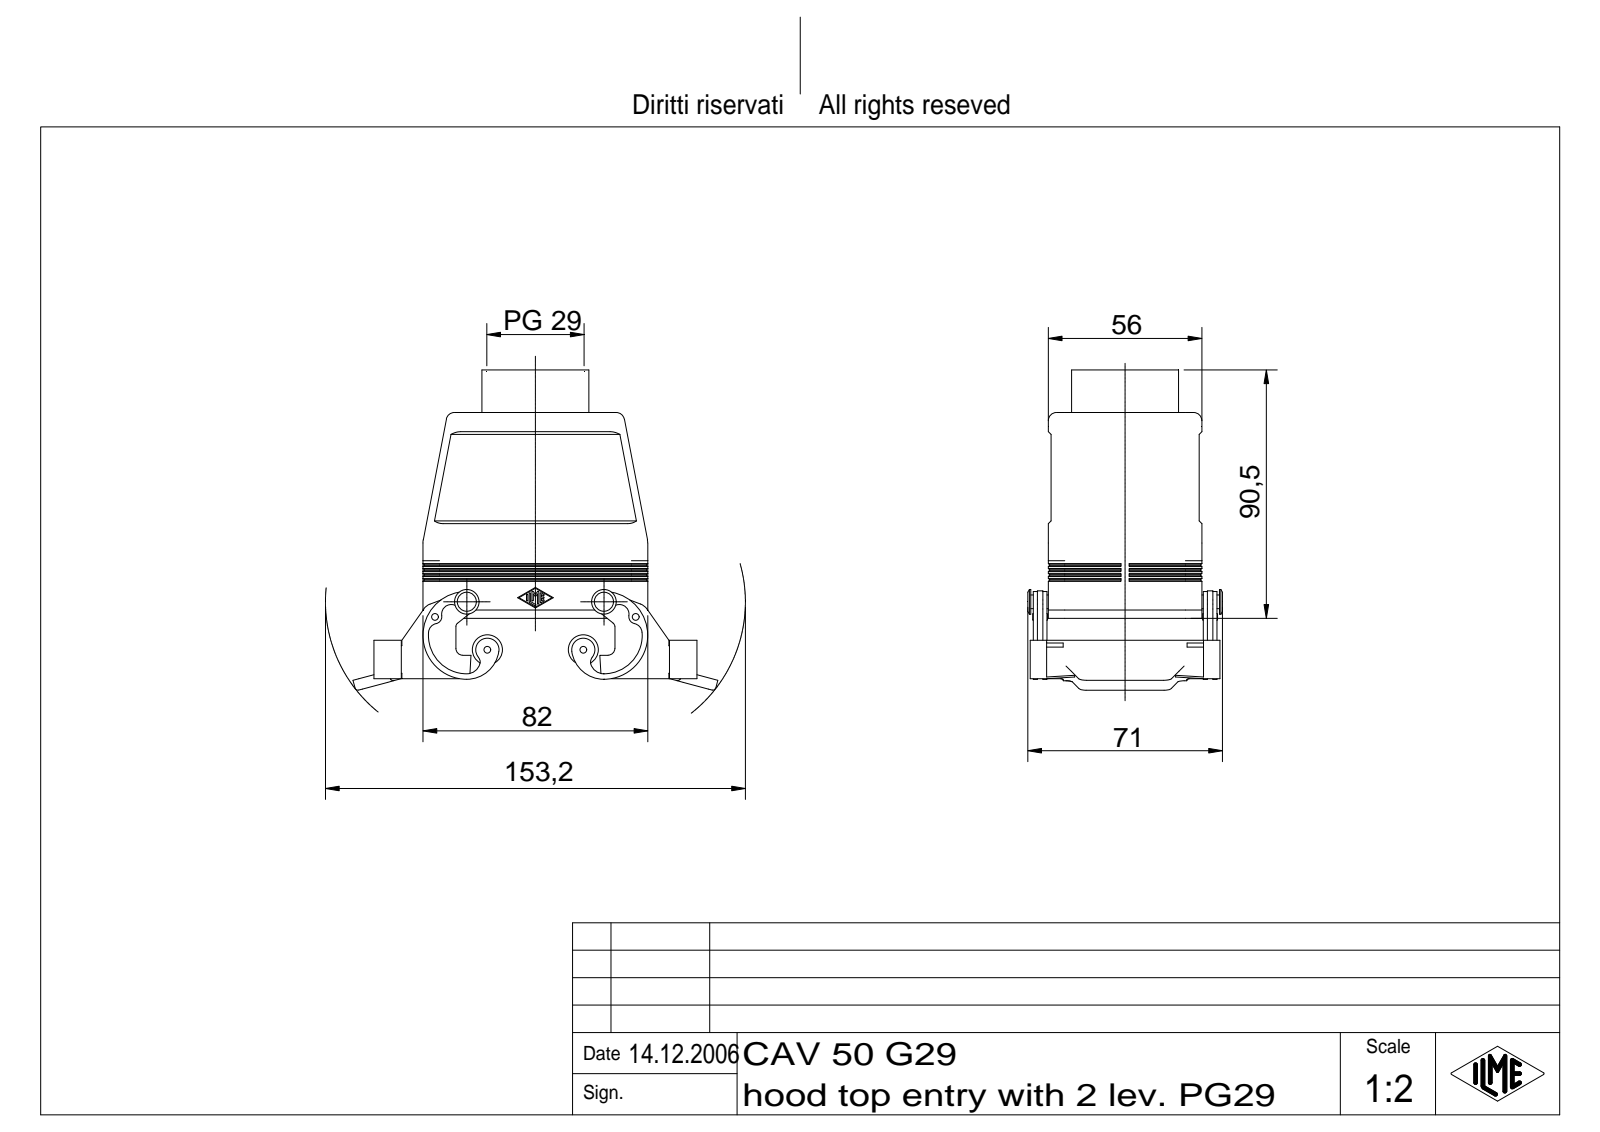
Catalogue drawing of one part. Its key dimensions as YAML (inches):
part_name: "CAV 50 G29"
step_written_by: "Autodesk Inventor 7 (AUTOMOTIVE_DESIGN)"
units: inches
bodies: {solids: 1, faces: 898, planar: 268, cylindrical: 260, other: 370}
overall_size: [5.239, 4.595, 2.795]
volume: 6.483
surface_area: 105.6
round_holes:
  - {diameter: 0.097, count: 4}
  - {diameter: 0.138, count: 4}
  - {diameter: 0.098, count: 2}
  - {diameter: 1.318, count: 1}
  - {diameter: 1.397, count: 1}
round_bosses_or_shafts:
  - {diameter: 0.433, count: 2}
  - {diameter: 0.354, count: 2}
  - {diameter: 0.197, count: 2}
  - {diameter: 0.079, count: 2}
  - {diameter: 1.929, count: 1}
  - {diameter: 1.535, count: 1}
  - {diameter: 1.378, count: 1}
partial_cylinders:
  - {radius: 0.01, count: 14}
  - {radius: 0.079, count: 14}
  - {radius: 0.236, count: 14}
  - {radius: 0.118, count: 12}
  - {radius: 0.039, count: 8}
  - {radius: 0.098, count: 6}
  - {radius: 0.138, count: 4}
  - {radius: 0.197, count: 4}
face_to_face_distances: [0.118, 1.969, 0.079, 2.087, 2.165, 2.047, 0.039, 2.205, 0.197, 0.443]
hole_center_spacings: [0.63, 1.309, 1.519, 2.598, 2.674, 2.882]
